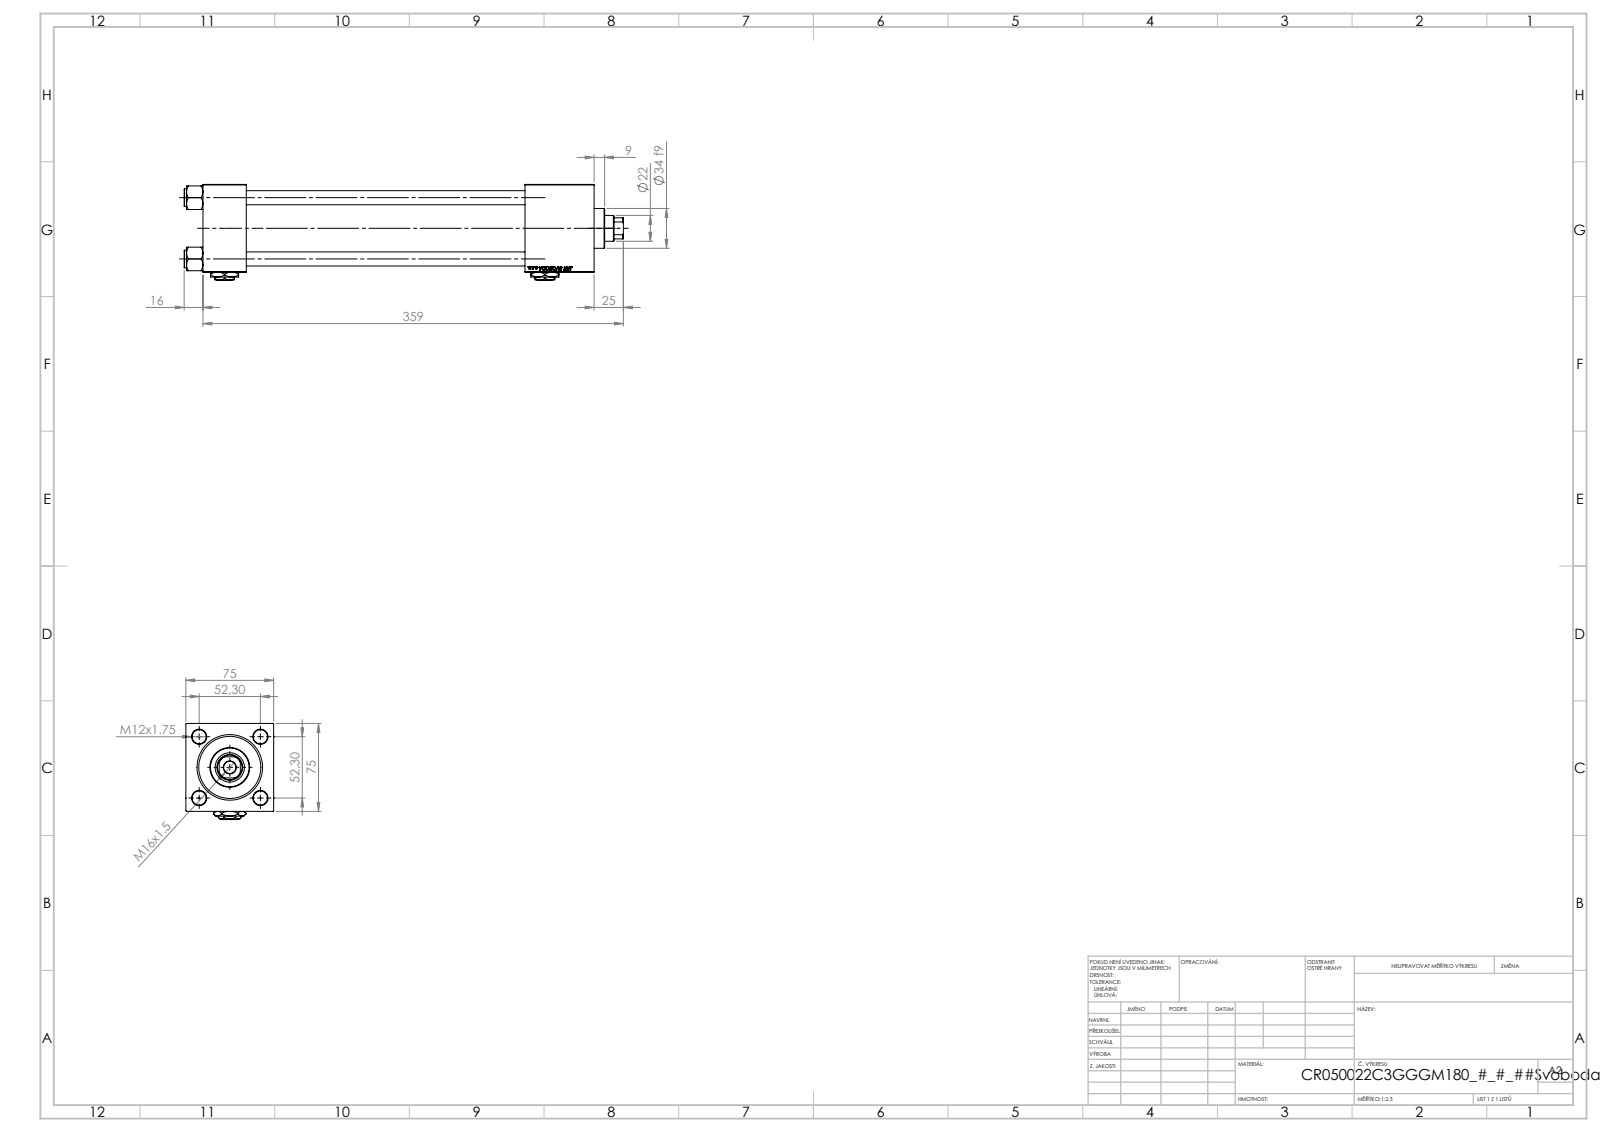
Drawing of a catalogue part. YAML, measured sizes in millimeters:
part_name: "Zatka_pro_OIL_PORT; V215CR_VCP_C; V215CR_C_TYCINKA; NUT_M5_C (+2 more)"
step_written_by: "SolidWorks 2019 (CONFIG_CONTROL_DESIGN)"
units: millimeters
bodies: {solids: 13, faces: 1249, planar: 573, cylindrical: 98, other: 578}
overall_size: [375, 82, 75.54]
volume: 891018
surface_area: 251404
round_holes:
  - {diameter: 12, count: 4}
  - {diameter: 7, count: 2}
  - {diameter: 20.96, count: 2}
  - {diameter: 30, count: 2}
  - {diameter: 10.5, count: 1}
  - {diameter: 22, count: 1}
  - {diameter: 25, count: 1}
  - {diameter: 41, count: 1}
  - {diameter: 50, count: 1}
  - {diameter: 53, count: 1}
round_bosses_or_shafts:
  - {diameter: 15, count: 4}
  - {diameter: 56, count: 1}
  - {diameter: 34, count: 1}
partial_cylinders:
  - {radius: 10.5, count: 1}
face_to_face_distances: [75, 37, 334, 297, 275, 59, 238, 305.3, 268.3, 30.3]
hole_center_spacings: [36.98, 52.3, 73.96, 273.5]
